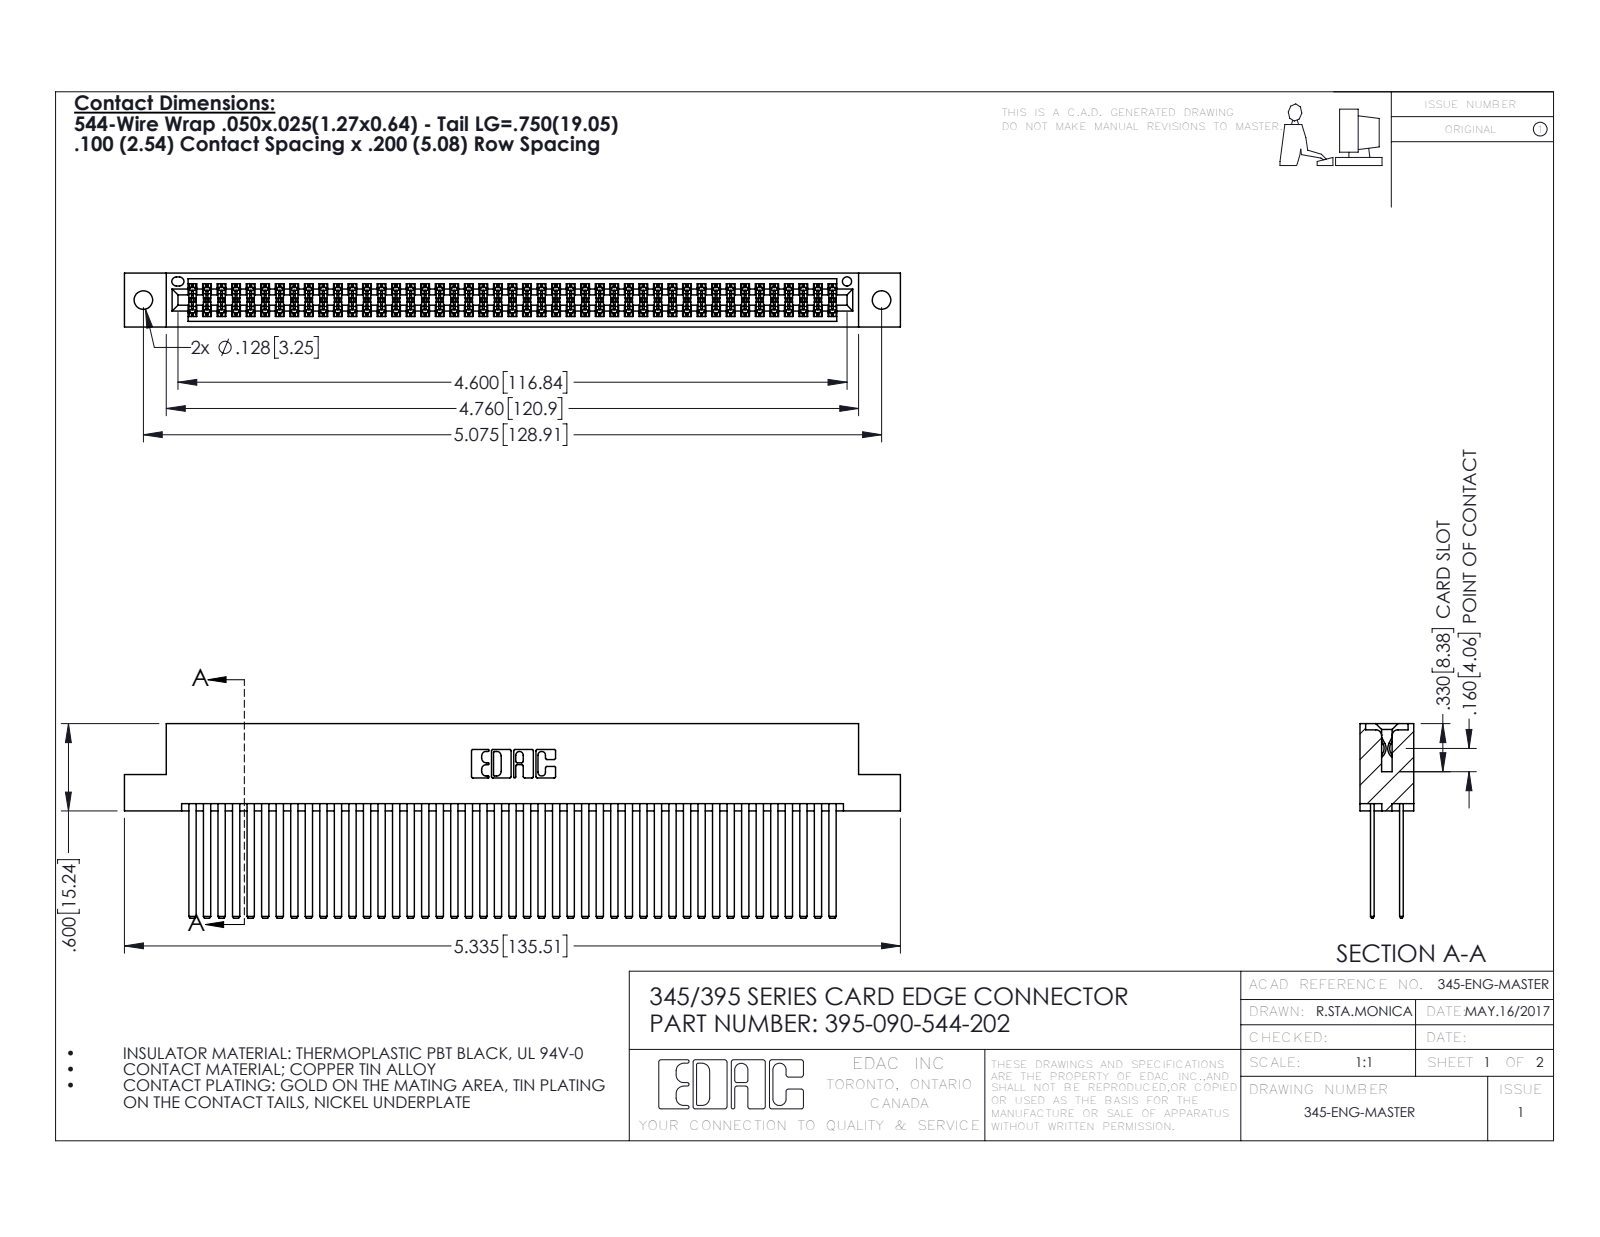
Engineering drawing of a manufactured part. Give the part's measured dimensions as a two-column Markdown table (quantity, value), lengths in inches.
| quantity | value |
| --- | --- |
| part name | 395-090-544-202; 345-292-001_345-293-144; 345 Part_Flush Mounting Lugs - 0.128 Dia |
| STEP written by | SolidWorks 2016 (CONFIG_CONTROL_DESIGN) |
| units | inches |
| bodies | 91 solids, 4086 faces (2690 planar, 1396 cylindrical, 0 other) |
| overall size | 5.335 × 1.337 × 0.37 |
| volume | 0.88 in³ |
| surface area | 38.43 in² |
| round holes (diameter × count) | 0.128 × 2, 0.064 × 1 |
| partial cylindrical surfaces (radius × count) | 0.006 × 135, 0.01 × 22, 0.007 × 6, 0.031 × 6, 0.026 × 3, 0.014 × 2, 0.019 × 2, 0.022 × 2 |
| main face-to-face distances | 0.2, 0.025, 0.298, 0.072, 0.098, 0.272, 0.225, 0.175, 0.37, 0.05 |
| hole center spacings | 0.27, 4.839, 5.075 |
